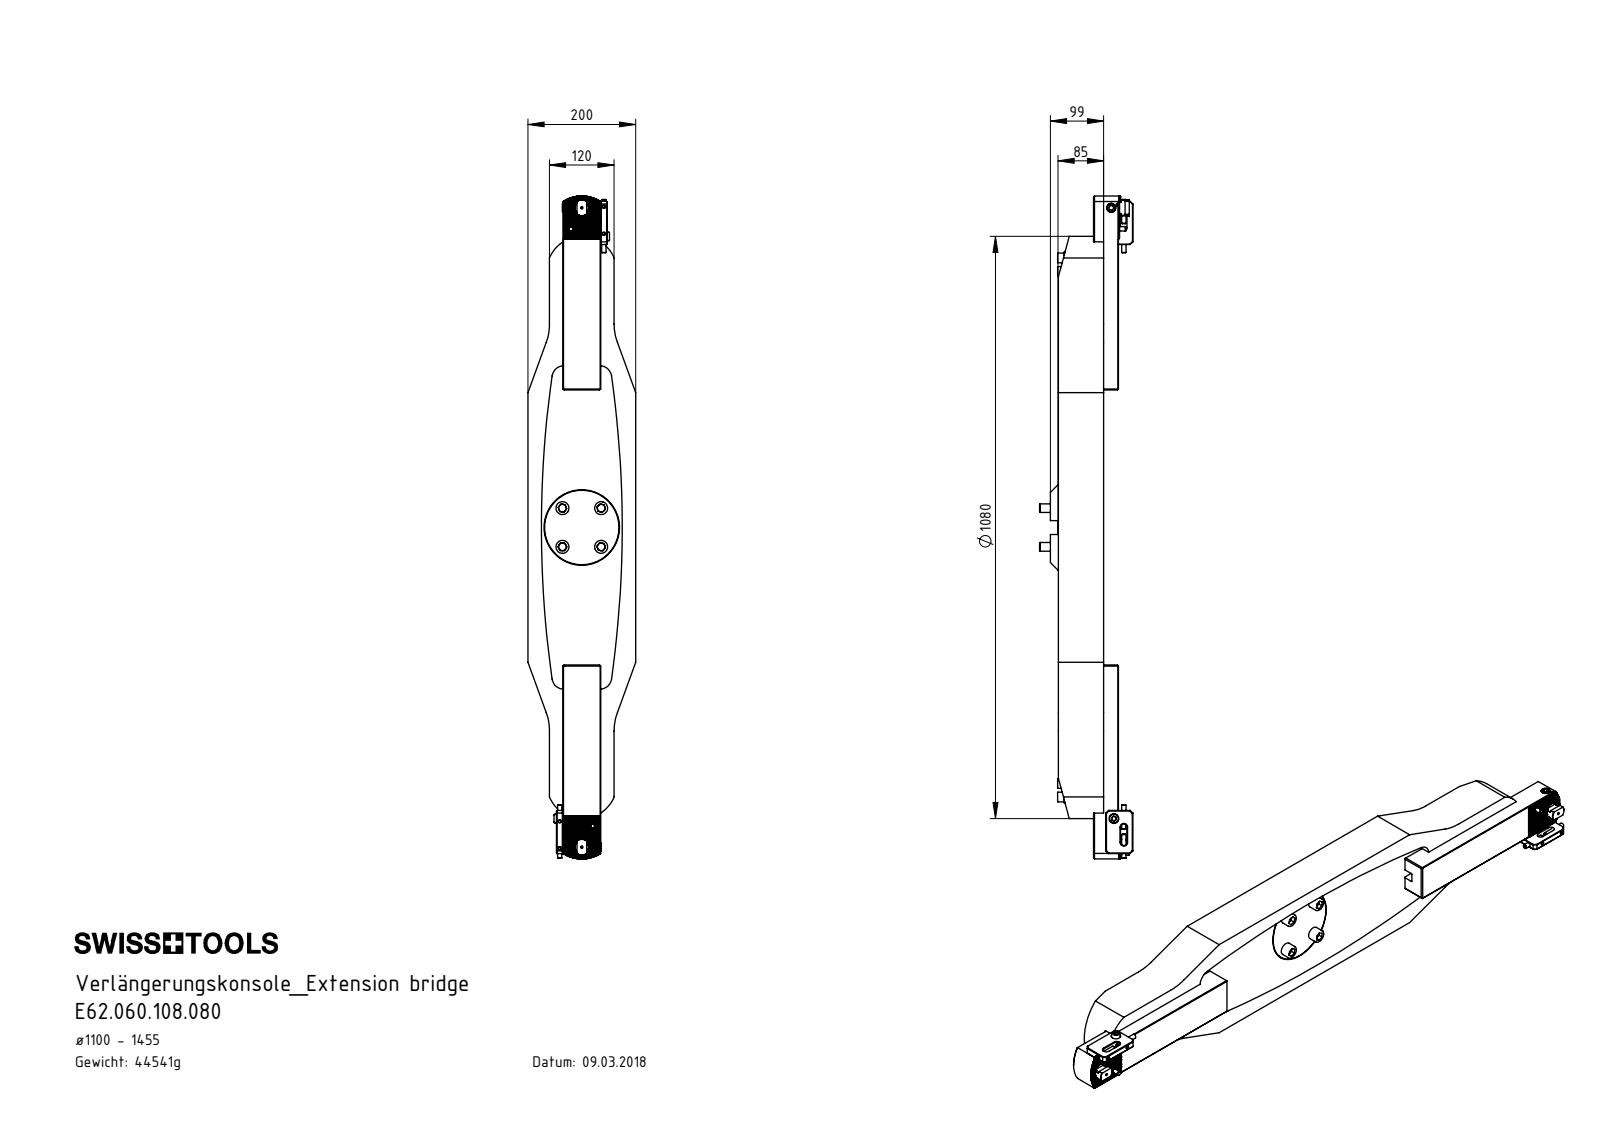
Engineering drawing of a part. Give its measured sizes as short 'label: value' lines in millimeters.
name: E62.060.108.080; DIN 179 - D12xD18x12; ISO 4762 - M16 x 80; VK3-ER1.001.005_A (+8 more)
written by: SolidWorks 2017 (CONFIG_CONTROL_DESIGN)
unit: mm
bodies: 46 solids, 2145 faces (916 planar, 736 cylindrical, 493 other)
size: 1230 × 200 × 173
volume: 11 790 000 mm³; area: 1 129 000 mm²
holes: 42× ⌀18, 40× ⌀10.2, 16× ⌀13, 4× ⌀5, 4× ⌀6, 4× ⌀6.8, 4× ⌀12, 4× ⌀17, 2× ⌀2, 2× ⌀8, 2× ⌀8.5, 2× ⌀10.5
bosses: 12× ⌀24, 8× ⌀16, 4× ⌀12, 2× ⌀10, 2× ⌀8, 1× ⌀138
rounds: 33× R0.14, 22× R2, 12× R22, 6× R15, 4× R1.5, 4× R5.5, 4× R6, 4× R8
face distances: 65, 40, 32, 135, 13, 45, 25, 44, 71, 20
hole spacings: 25, 47.17, 50, 64.03, 40, 75, 85, 925
